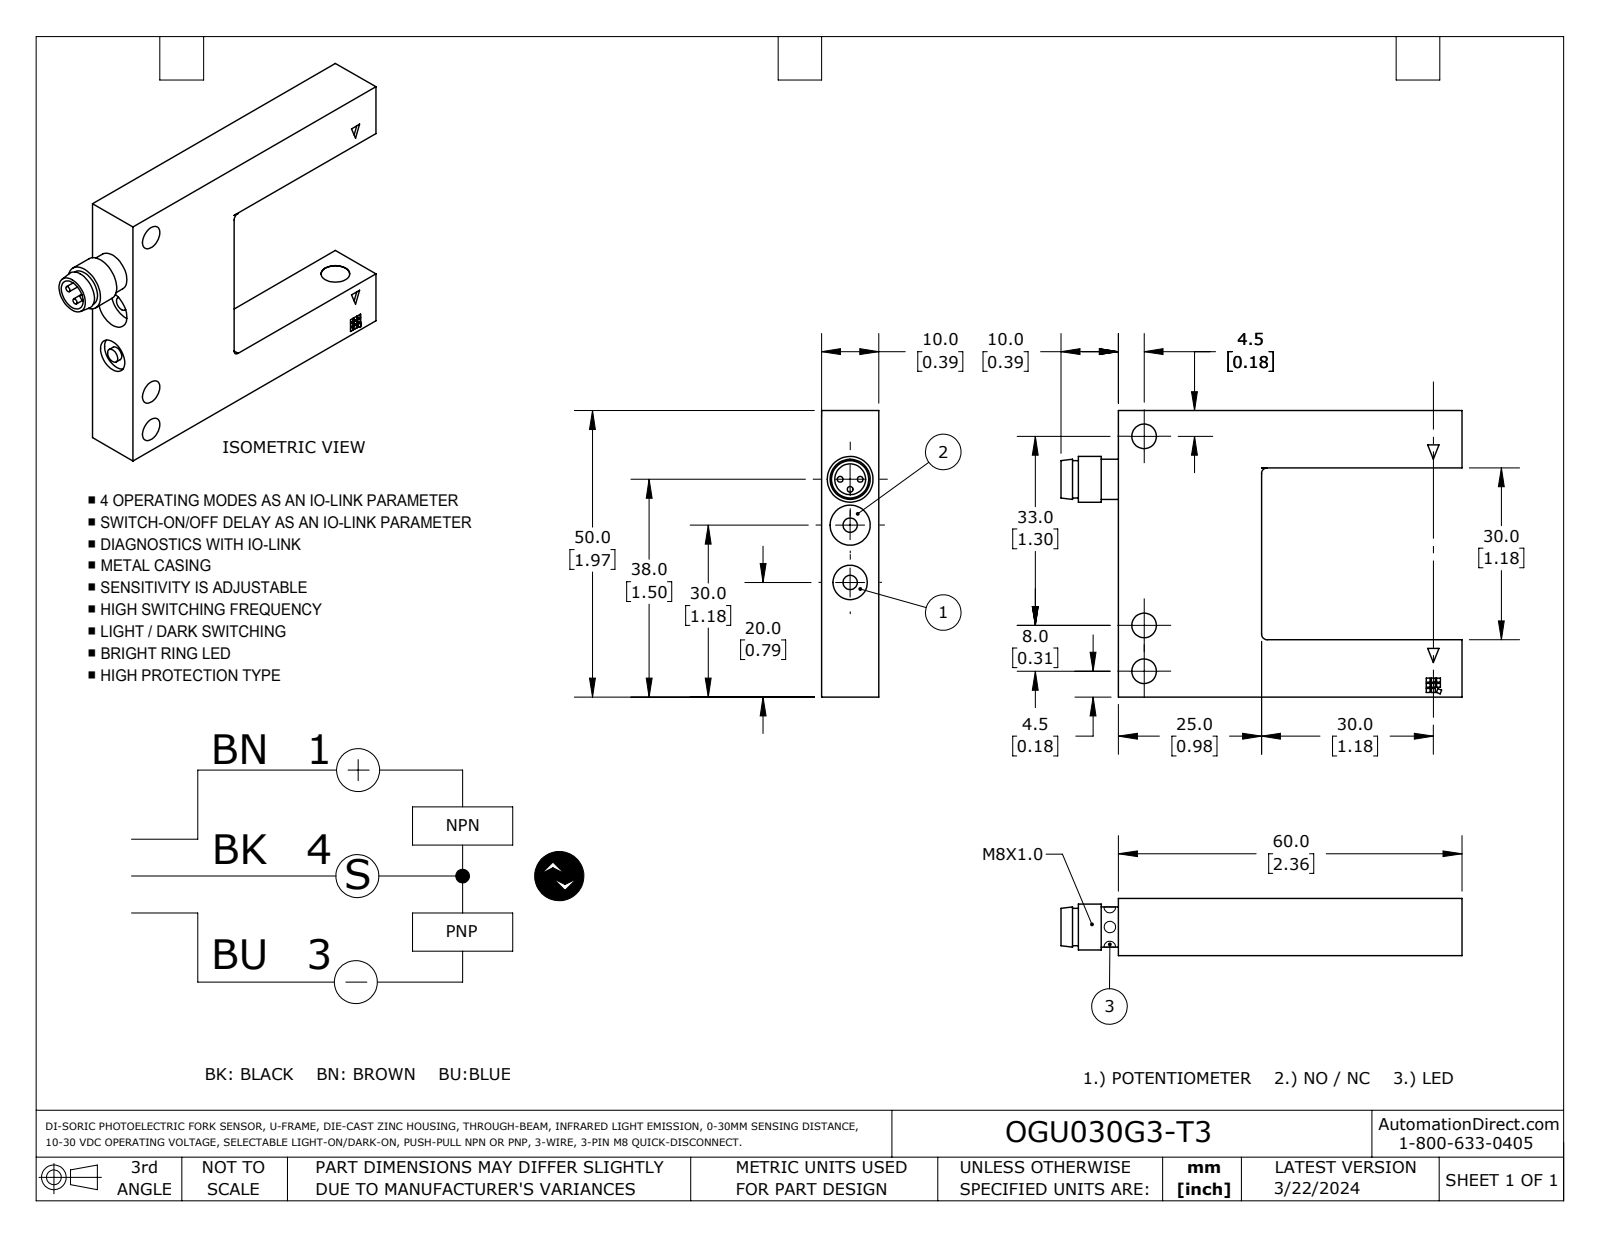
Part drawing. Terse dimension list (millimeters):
name: OGU030G3-T3
written by: SolidWorks 2023 (AUTOMOTIVE_DESIGN)
unit: mm
bodies: 1 solid, 112 faces (91 planar, 20 cylindrical, 1 other)
size: 70 × 50 × 10
volume: 19 240 mm³; area: 7 639 mm²
holes: 3× ⌀4.3, 1× ⌀3, 1× ⌀5, 1× ⌀5.4, 1× ⌀6, 1× ⌀7
bosses: 3× ⌀1, 2× ⌀2.5, 1× ⌀8, 1× ⌀7, 1× ⌀6.5
rounds: 3× R1
face distances: 10, 40, 50, 30, 25, 35, 60, 10, 1, 40.1
hole spacings: 8, 10, 18, 33, 41
